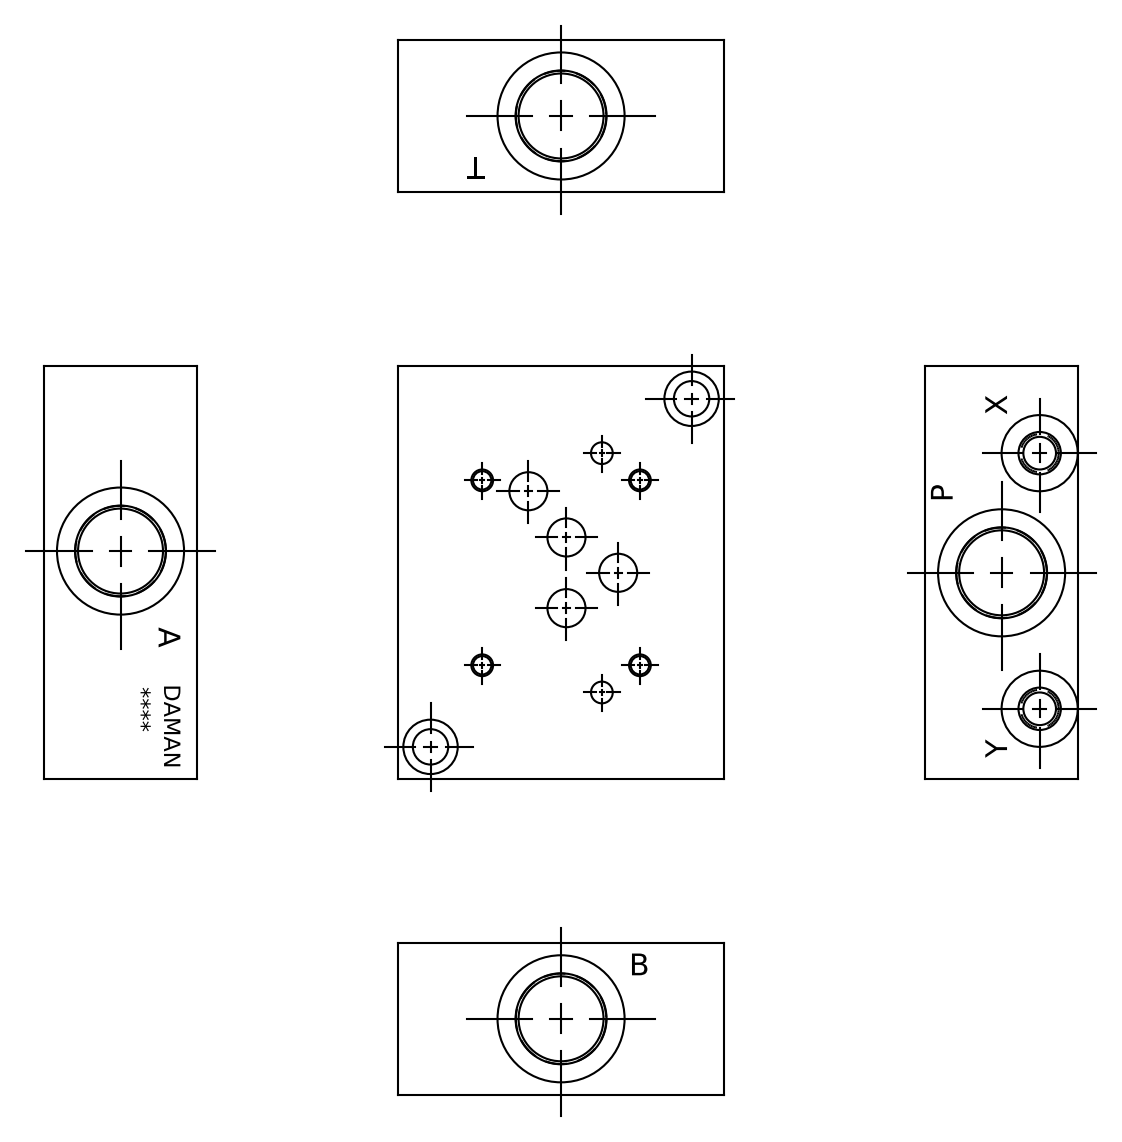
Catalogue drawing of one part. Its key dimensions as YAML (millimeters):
part_name: "Part_DD05HESPS12B_3D"
step_written_by: "Autodesk Inventor 2019 (AUTOMOTIVE_DESIGN)"
units: millimeters
bodies: {solids: 1, faces: 536, planar: 342, cylindrical: 43, other: 151}
overall_size: [120.65, 95.25, 44.45]
volume: 425502
surface_area: 59347
round_holes:
  - {diameter: 5, count: 4}
  - {diameter: 5.99, count: 4}
  - {diameter: 23.01, count: 3}
  - {diameter: 24.41, count: 3}
  - {diameter: 26.54, count: 3}
  - {diameter: 37.11, count: 3}
  - {diameter: 4.78, count: 2}
  - {diameter: 10.72, count: 2}
  - {diameter: 11.1, count: 2}
  - {diameter: 11.11, count: 2}
  - {diameter: 11.13, count: 2}
  - {diameter: 11.68, count: 2}
face_to_face_distances: [44.45, 95.25, 120.65, 0.79, 94.46, 119.86, 93.67, 119.07, 89.5, 88.71]
hole_center_spacings: [18.27, 6.34, 13.64, 13.65, 13.89, 17.48, 20.64, 24.15]
